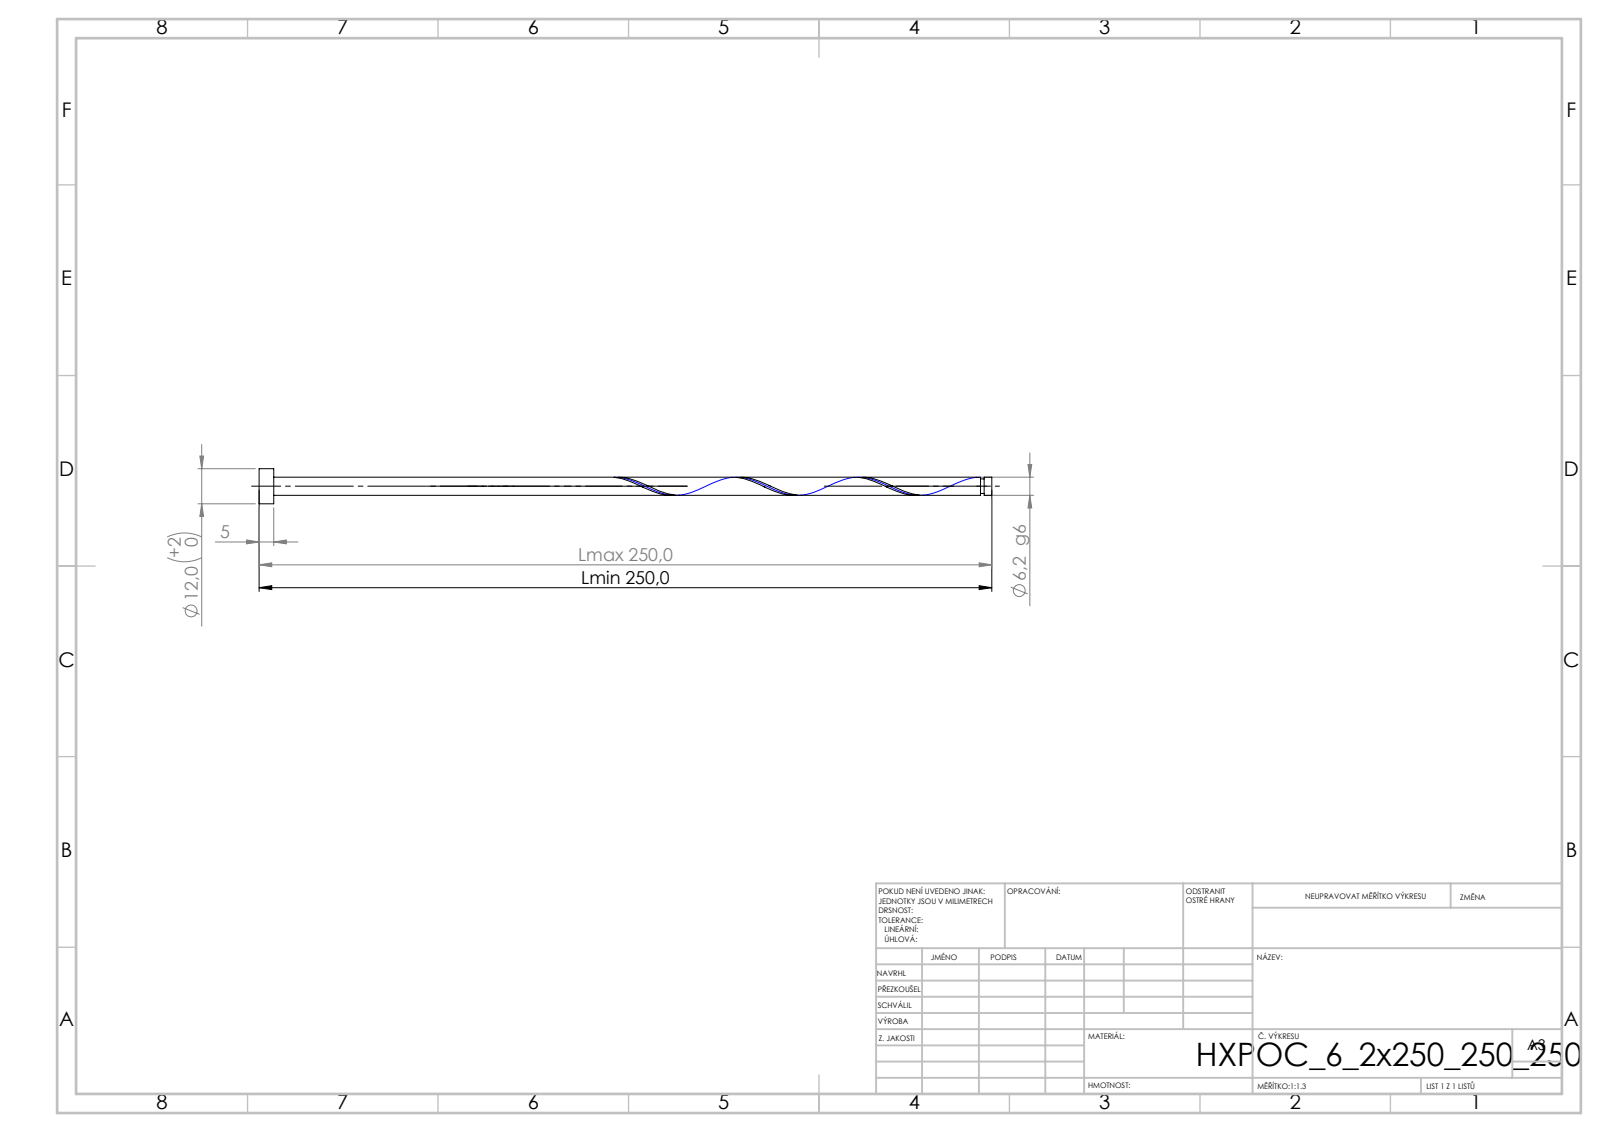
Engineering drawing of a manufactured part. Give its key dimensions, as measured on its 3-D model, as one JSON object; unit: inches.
{"step_written_by": "SolidWorks 2019 (CONFIG_CONTROL_DESIGN)", "units": "inches", "bodies": {"solids": 1, "faces": 21, "planar": 6, "cylindrical": 14, "other": 1}, "overall_size": [9.843, 0.472, 0.472], "volume_in3": 0.481, "surface_area_in2": 8.196, "round_bosses_or_shafts": [[0.472, 1], [0.244, 1], [0.195, 1]], "face_to_face_distances": [0.197, 9.843, 9.646, 9.741, 9.544, 0.102, 9.692, 9.495, 0.049, 0.15]}
